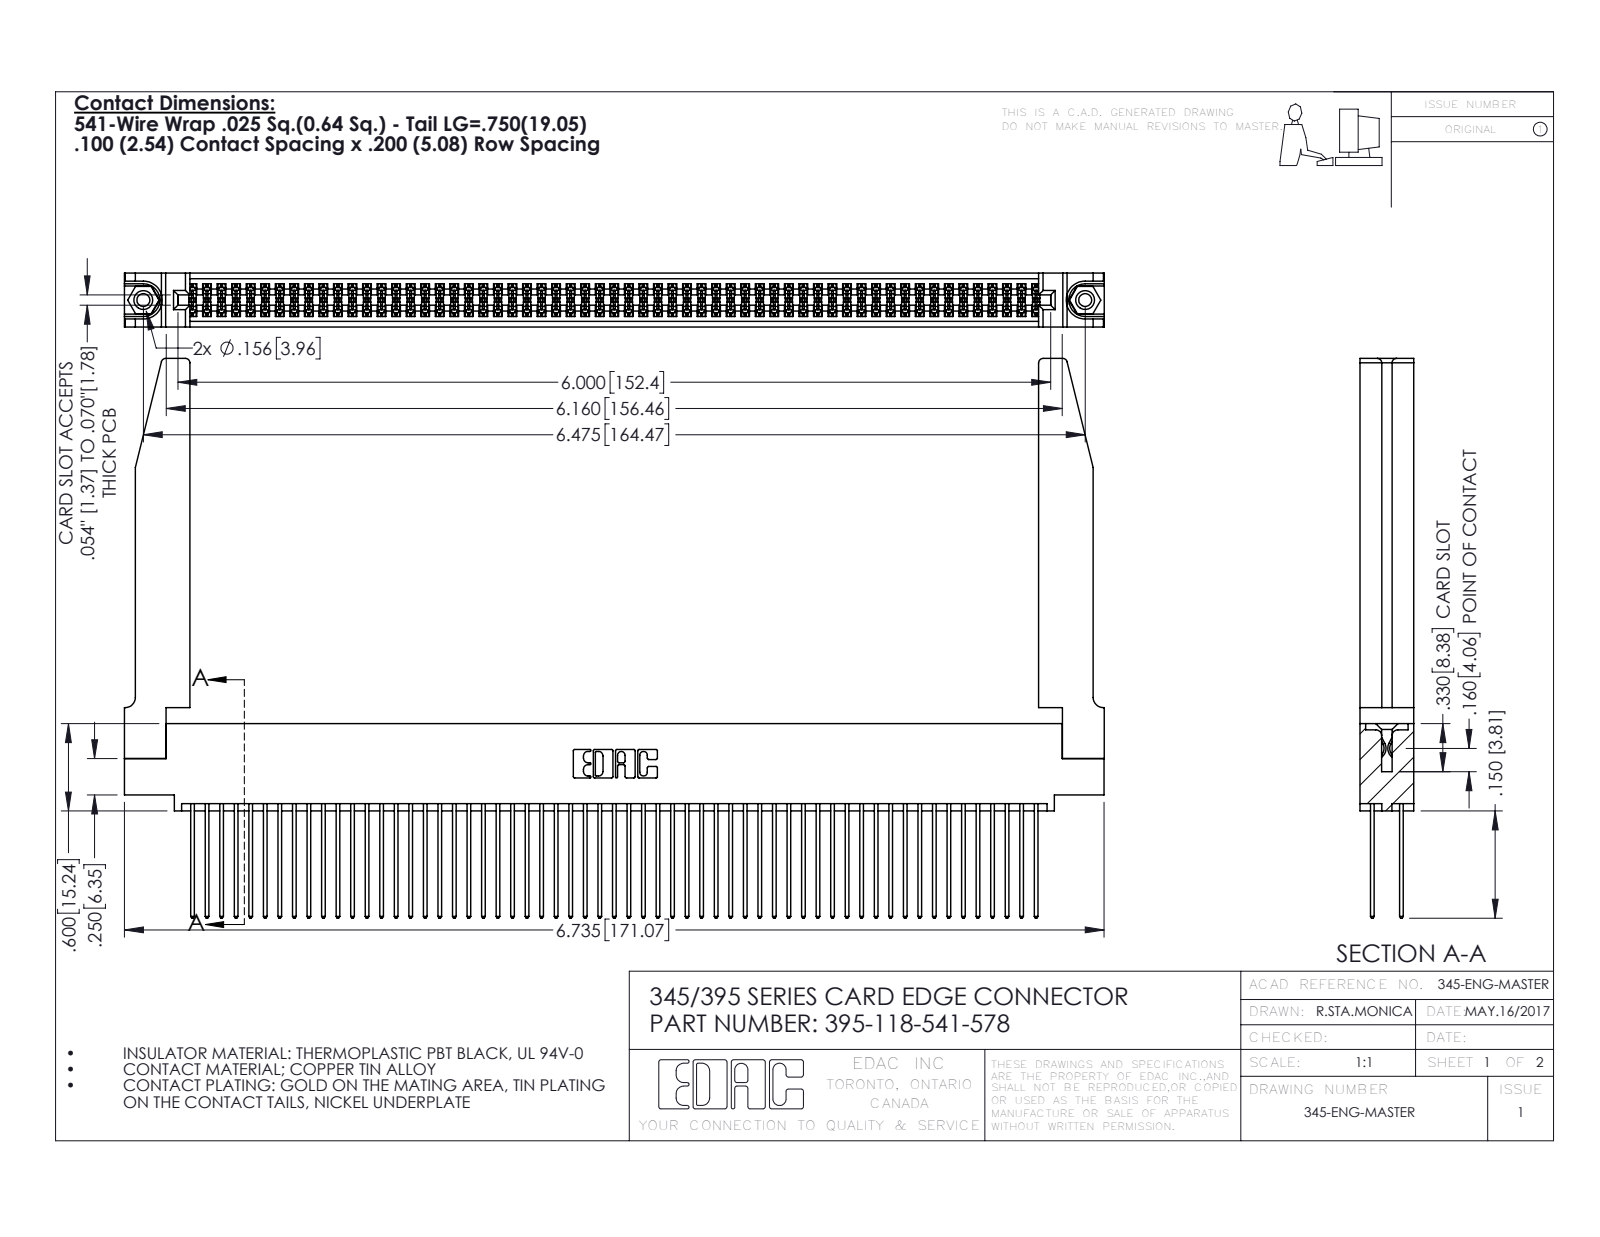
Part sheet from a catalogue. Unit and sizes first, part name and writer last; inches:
Units: inches
Overall size (bounding box): 6.736 × 3.847 × 0.37
Round holes (diameter × count): ⌀0.089 ×2, ⌀0.125 ×2, ⌀0.156 ×2, ⌀0.064 ×1
Round bosses / shafts (diameter × count): ⌀0.155 ×2
Partial cylindrical surfaces — rounded edges, fillets, slot ends (radius × count): R0.006 ×177, R0.01 ×118, R0.01 ×22, R0.03 ×8, R0.007 ×6, R0.031 ×6, R0.026 ×3, R0.014 ×2
Main face-to-face distances: 0.072, 0.298, 0.37, 0.098, 0.272, 0.025, 0.2, 0.225, 0.175, 0.148
Hole centre spacings: 0.27, 6.239, 6.475
Volume: 1.535 in³ · Surface area: 56.01 in²
Bodies: 123 solids, 6264 faces (4120 planar, 2092 cylindrical, 52 other)
Part name (STEP PRODUCT): 345-220-078_345-220-078; 345-292-001_345-293-141; 395-118-541-578; 345 Part_0.110 Offset - 0.156 Dia-TH (+1 more)
STEP written by: SolidWorks 2016 (CONFIG_CONTROL_DESIGN)
